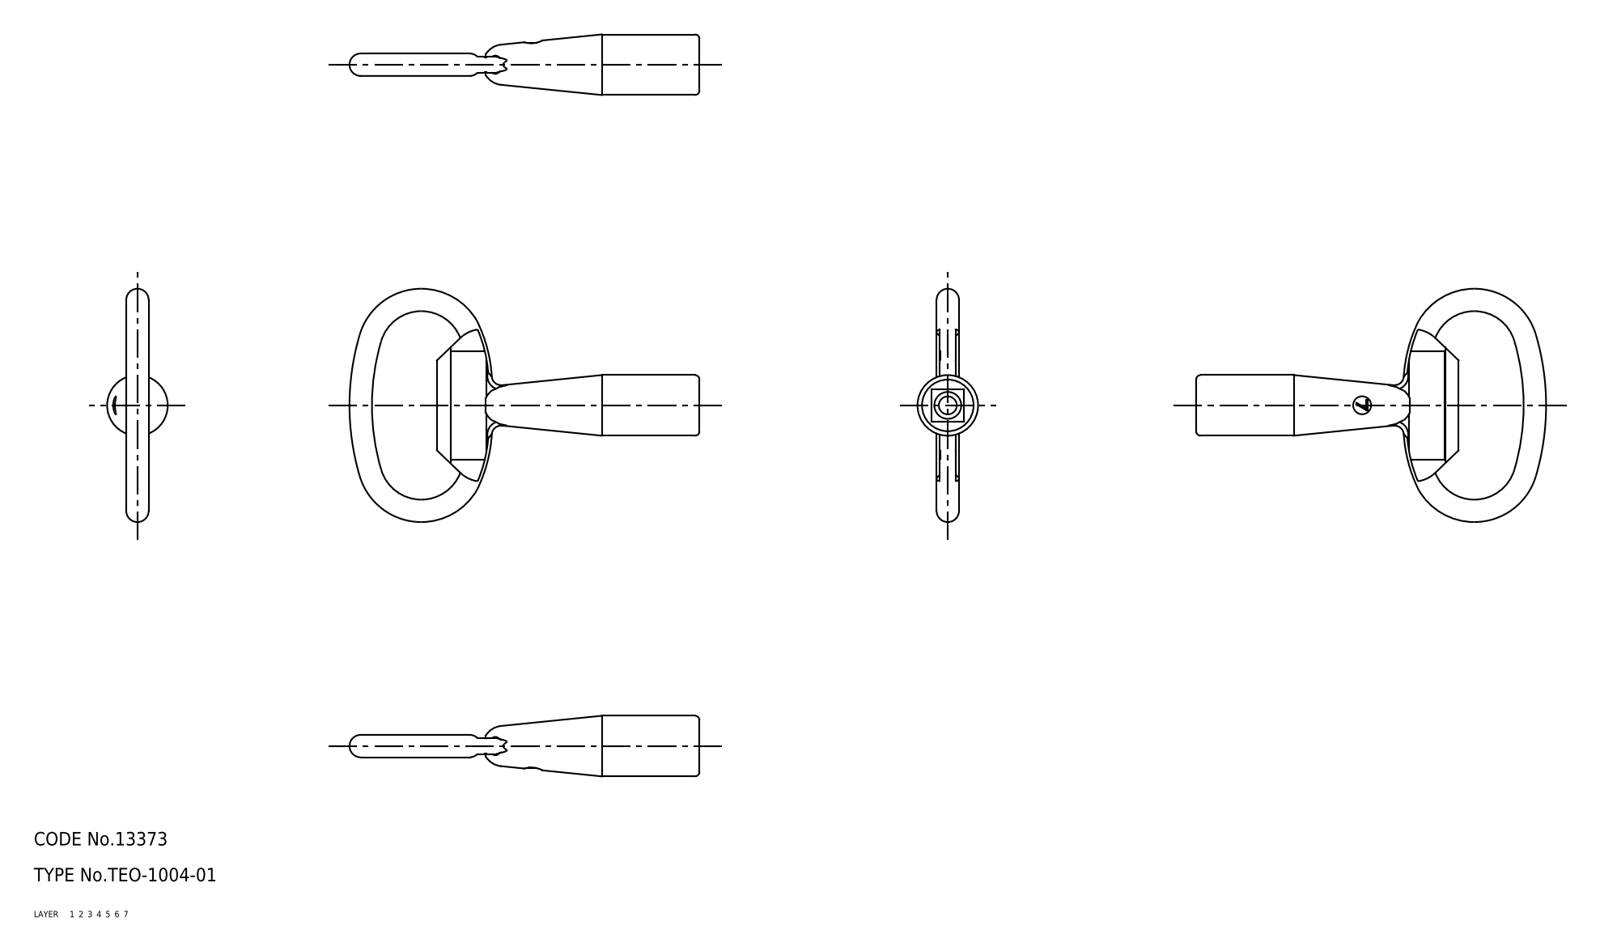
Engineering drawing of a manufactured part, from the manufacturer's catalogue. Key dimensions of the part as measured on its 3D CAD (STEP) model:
Part name (STEP PRODUCT): key
STEP written by: CADfix (AUTOMOTIVE_DESIGN)
Units: millimetres
Bodies: 1 solid, 57 faces (0 planar, 0 cylindrical, 57 other)
Overall size (bounding box): 78 × 52 × 13.5
Volume: 7 451 mm³ · Surface area: 4 686 mm²
